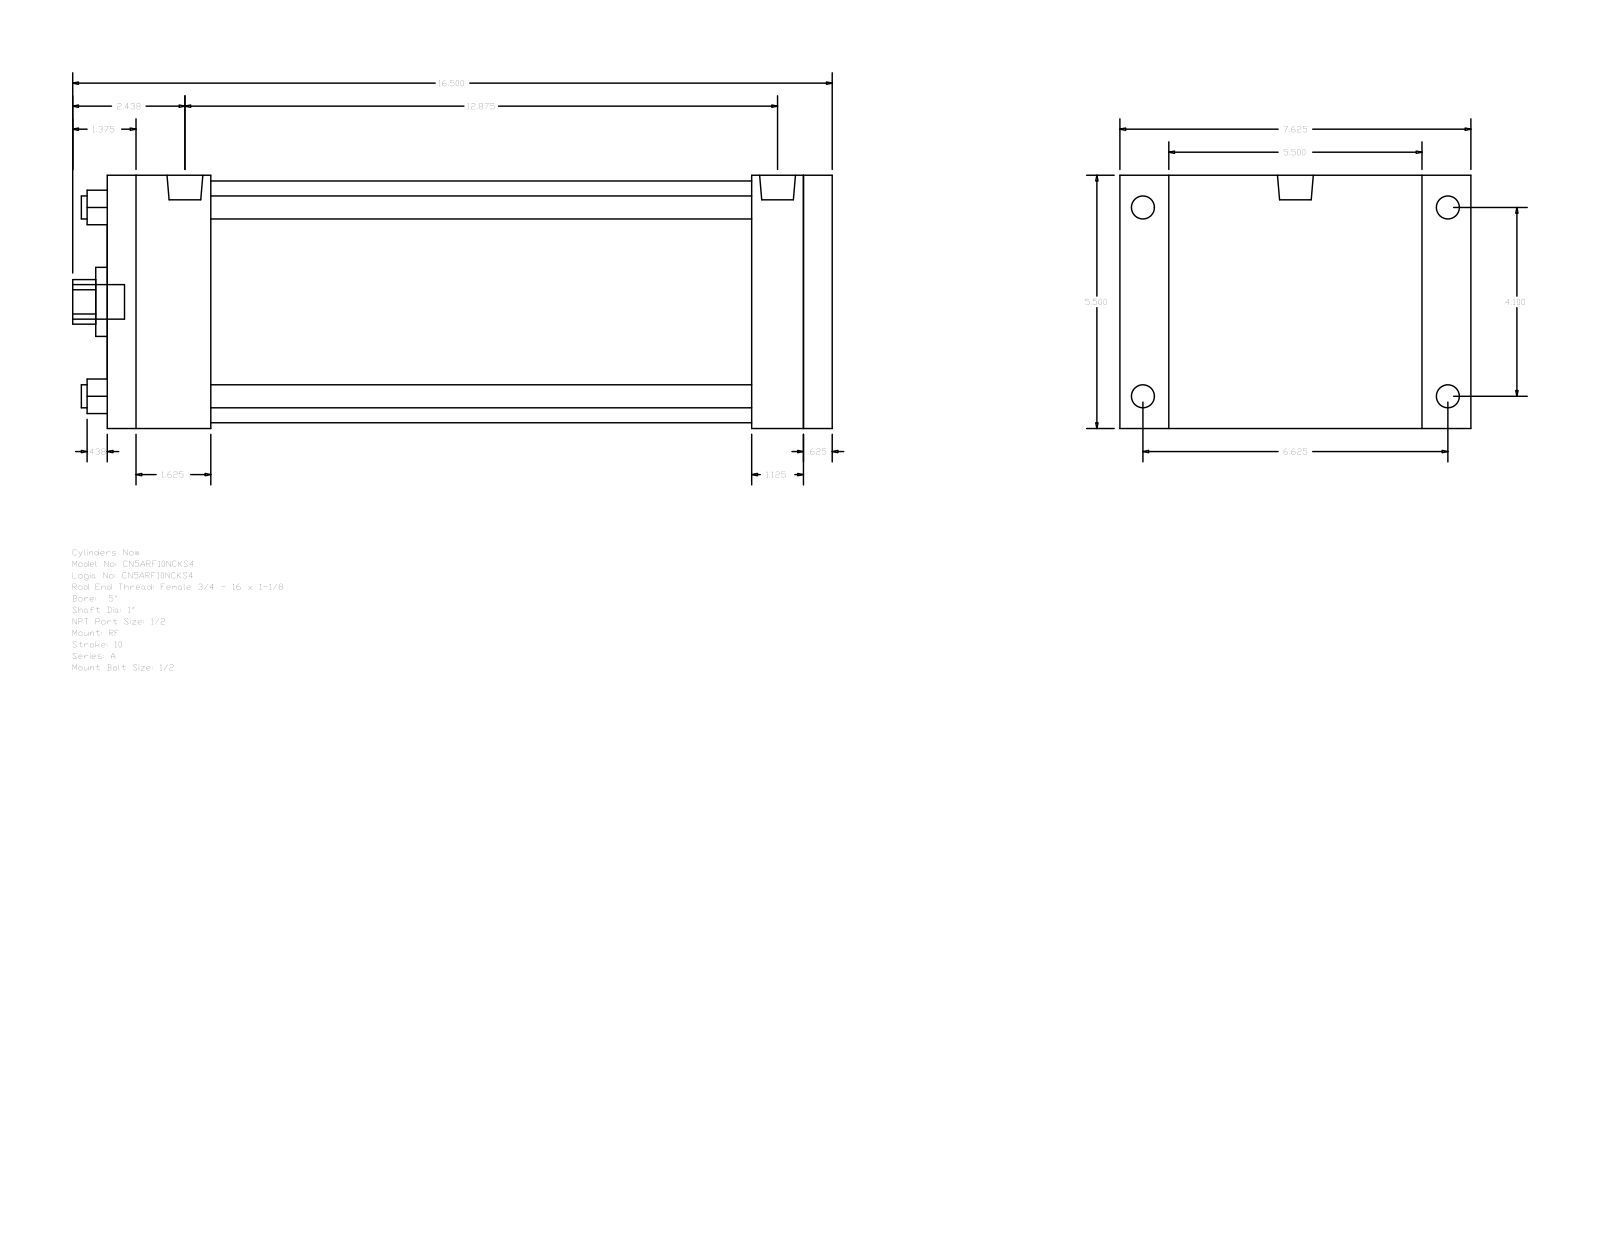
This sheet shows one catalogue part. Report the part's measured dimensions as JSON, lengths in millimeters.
{"part_name": "A_RF__0500_1", "step_written_by": "GSSL Pune (CONFIG_CONTROL_DESIGN)", "units": "millimeters", "bodies": {"solids": 0, "faces": 92, "planar": 64, "cylindrical": 28, "other": 0}, "overall_size": [419.1, 193.68, 139.7], "round_holes": [[12.7, 4], [25.4, 1], [38.1, 1], [133.35, 1]], "round_bosses_or_shafts": [[12.7, 4], [8.73, 4], [19.77, 2], [19.05, 1]], "partial_cylinders_radius": [[12.29, 1]], "face_to_face_distances": [139.7, 400.05, 15.87, 384.18, 57.15, 327.03, 342.9, 355.6, 298.45, 28.58], "hole_center_spacings": [73.64, 104.14, 147.28]}
